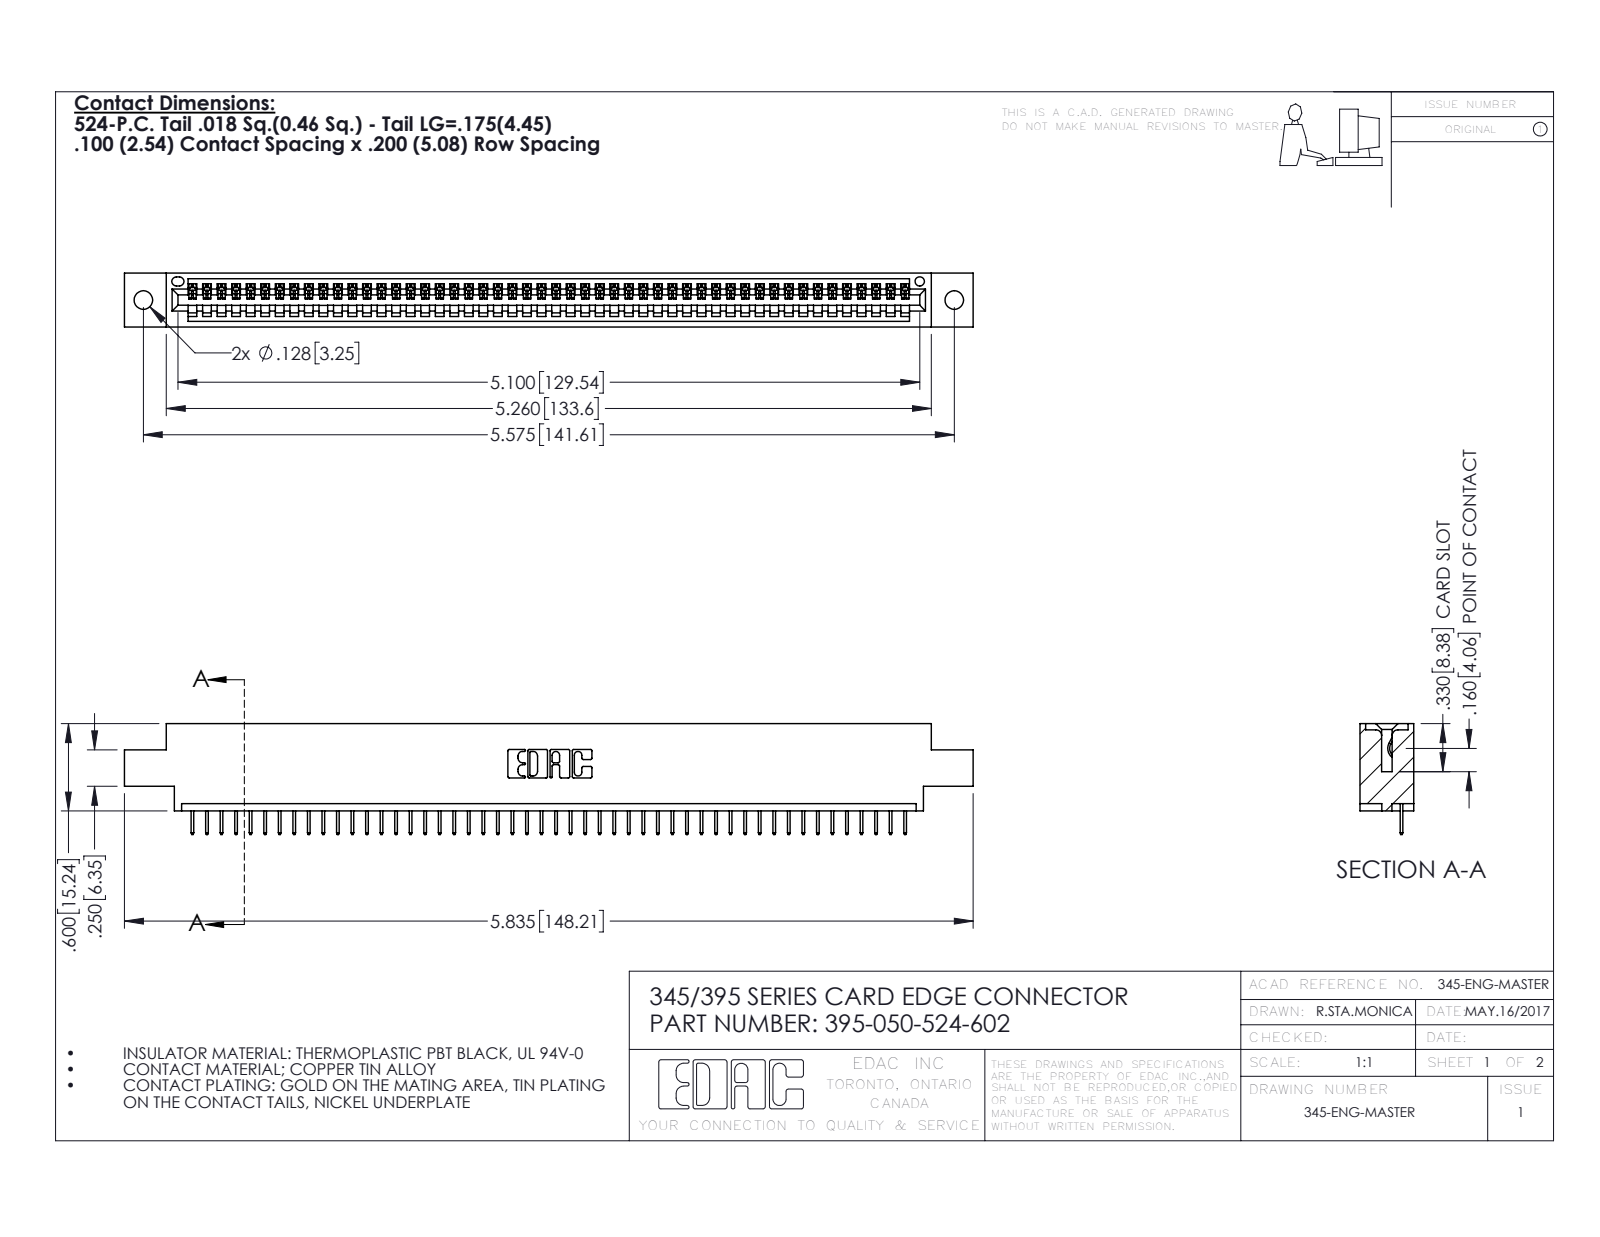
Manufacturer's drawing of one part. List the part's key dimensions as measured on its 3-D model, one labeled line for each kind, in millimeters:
Part name (STEP PRODUCT): 345 Part_0.170 Offset - 0.128 Dia; 395-050-524-602; 345-292-001_345-293-124
STEP written by: SolidWorks 2016 (CONFIG_CONTROL_DESIGN)
Units: millimetres
Bodies: 51 solids, 3230 faces (2384 planar, 846 cylindrical, 0 other)
Overall size (bounding box): 148.2 × 19.4 × 9.4
Volume: 13 800 mm³ · Surface area: 17 660 mm²
Round holes (diameter × count): ⌀3.3 ×2, ⌀1.6 ×1
Partial cylindrical surfaces — rounded edges, fillets, slot ends (radius × count): R0.2 ×100, R0.3 ×22, R0.2 ×6, R0.8 ×6, R0.7 ×3, R0.8 ×2, R1 ×2, R0.4 ×1
Main face-to-face distances: 1.8, 7.6, 9.4, 5.1, 2.5, 6.9, 0.6, 5.7, 1.8, 4.4
Hole centre spacings: 6.9, 135.6, 141.6
